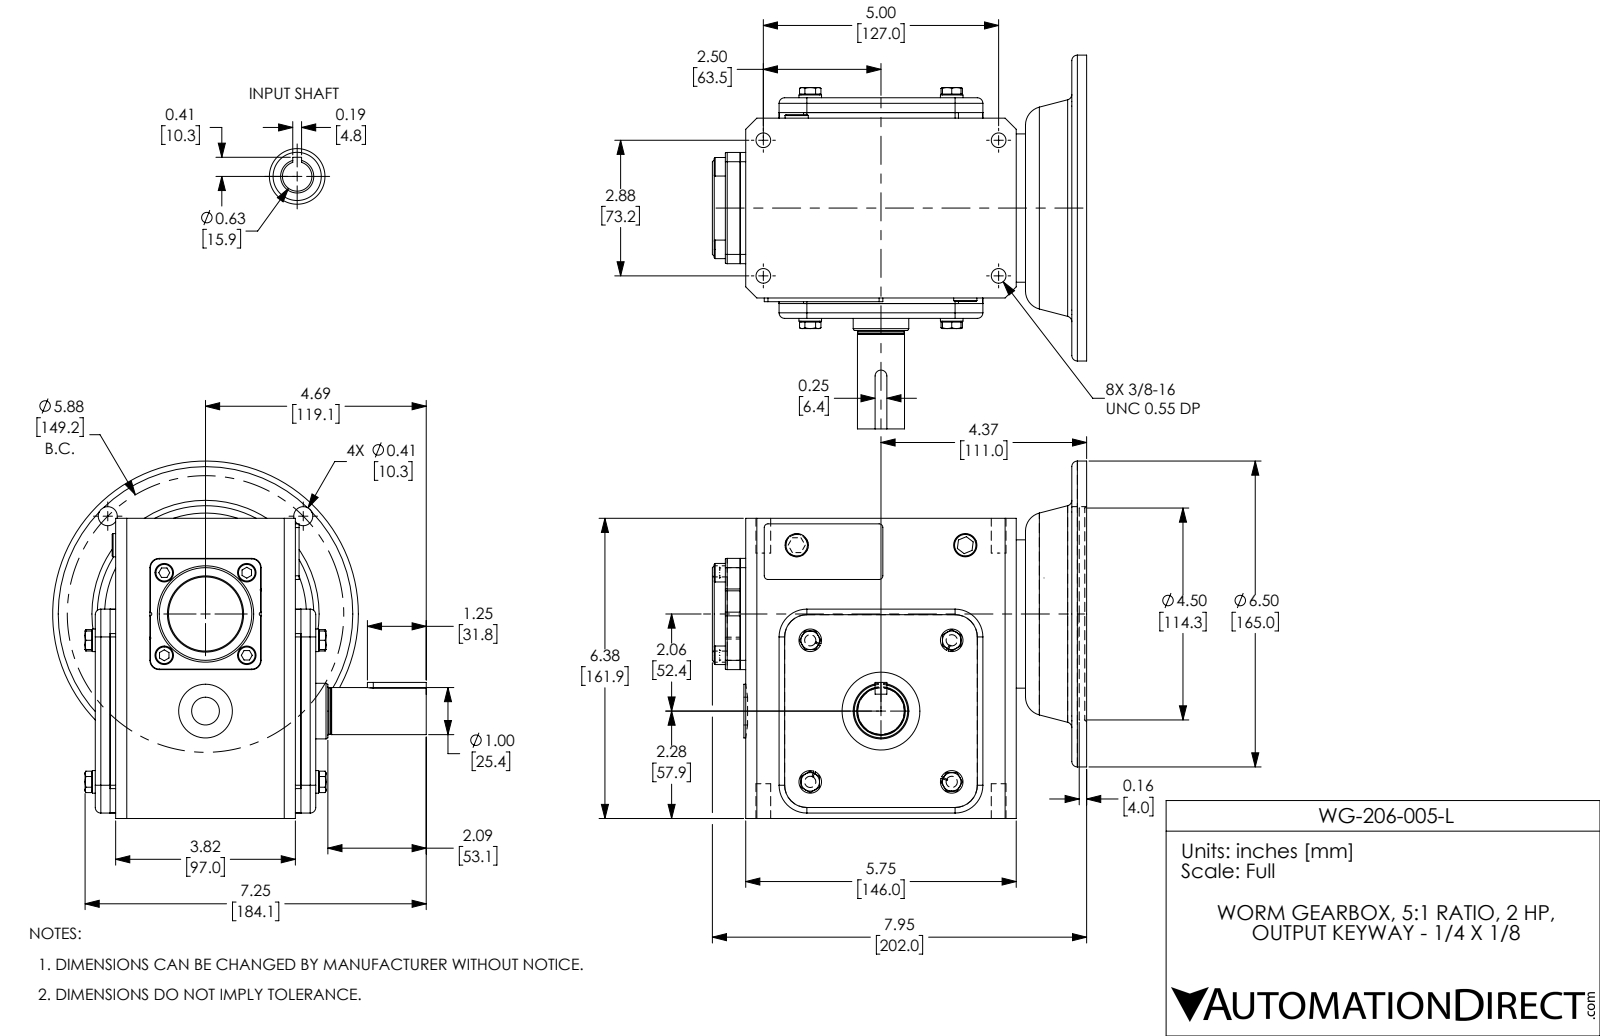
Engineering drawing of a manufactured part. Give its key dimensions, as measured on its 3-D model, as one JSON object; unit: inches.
{"part_name": "WG-206-005-L", "step_written_by": "SolidWorks 2017 (AUTOMOTIVE_DESIGN)", "units": "inches", "bodies": {"solids": 44, "faces": 619, "planar": 303, "cylindrical": 188, "other": 128}, "overall_size": [7.953, 7.938, 7.591], "volume_in3": 169.4, "surface_area_in2": 418.2, "round_holes": [[0.313, 4], [0.406, 4], [0.495, 2], [1.181, 2], [0.591, 1], [0.625, 1], [1.457, 1], [1.654, 1], [3.543, 1], [4.5, 1]], "round_bosses_or_shafts": [[0.394, 8], [0.48, 4], [6.496, 1], [3.15, 1], [2.047, 1], [1.575, 1], [1.142, 1], [1, 1]], "partial_cylinders_radius": [[0.079, 8], [0.118, 8], [0.197, 4], [0.591, 4], [0.02, 2], [0.039, 2], [0.125, 1], [2.717, 1]], "face_to_face_distances": [0.315, 0.118, 4.055, 4.37, 0.433, 3.937, 4.252, 6.375, 4.685, 0.709], "hole_center_spacings": [2.937, 4.154, 2.077, 2.681, 2.88, 4.631, 5, 5.77]}
